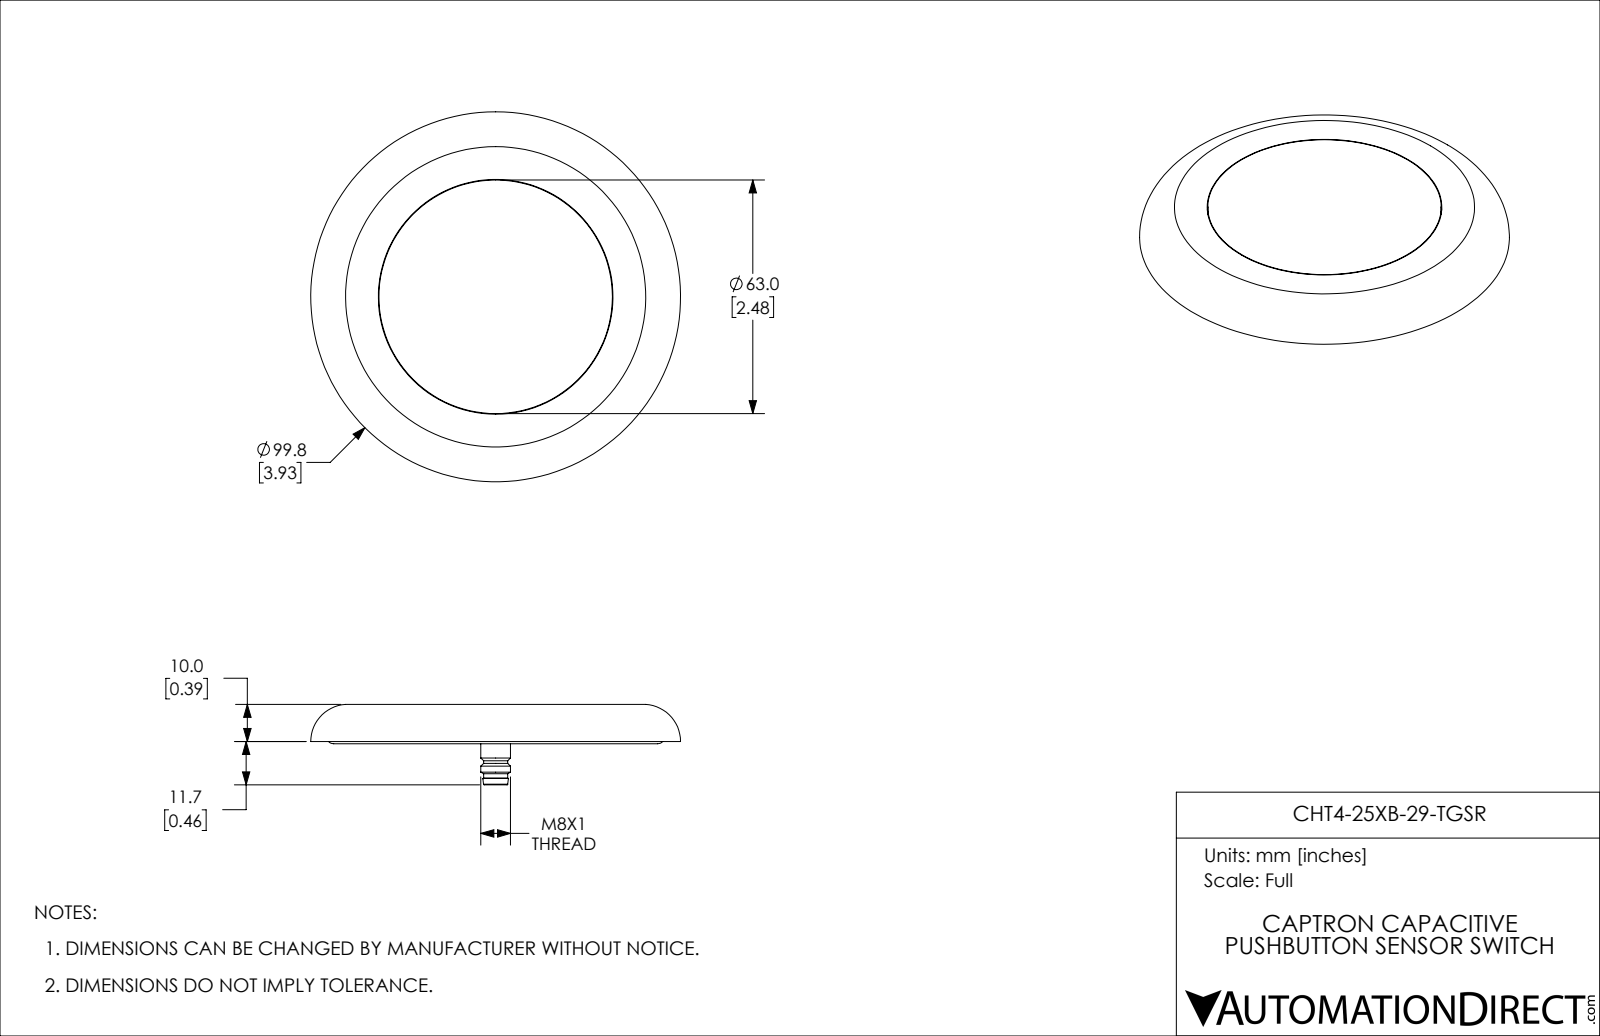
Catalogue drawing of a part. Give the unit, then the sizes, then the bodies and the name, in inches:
Units: inches
Overall size (bounding box): 3.929 × 3.929 × 0.854
Round holes (diameter × count): ⌀0.228 ×1, ⌀2.299 ×1, ⌀2.493 ×1, ⌀2.543 ×1
Round bosses / shafts (diameter × count): ⌀0.039 ×5, ⌀2.48 ×1, ⌀0.315 ×1, ⌀0.256 ×1
Partial cylindrical surfaces — rounded edges, fillets, slot ends (radius × count): R0.02 ×2, R0.039 ×1, R1.26 ×1
Main face-to-face distances: 0.326, 0.056, 0.382, 0.057, 0.324, 0.269, 0.057, 0.064, 0.332, 0.39
Hole centre spacings: 0.126
Volume: 1.761 in³ · Surface area: 64 in²
Bodies: 9 solids, 106 faces (25 planar, 35 cylindrical, 46 other)
Part name (STEP PRODUCT): CHT4-25XB-29-TGSR
STEP written by: SolidWorks 2019 (CONFIG_CONTROL_DESIGN)
